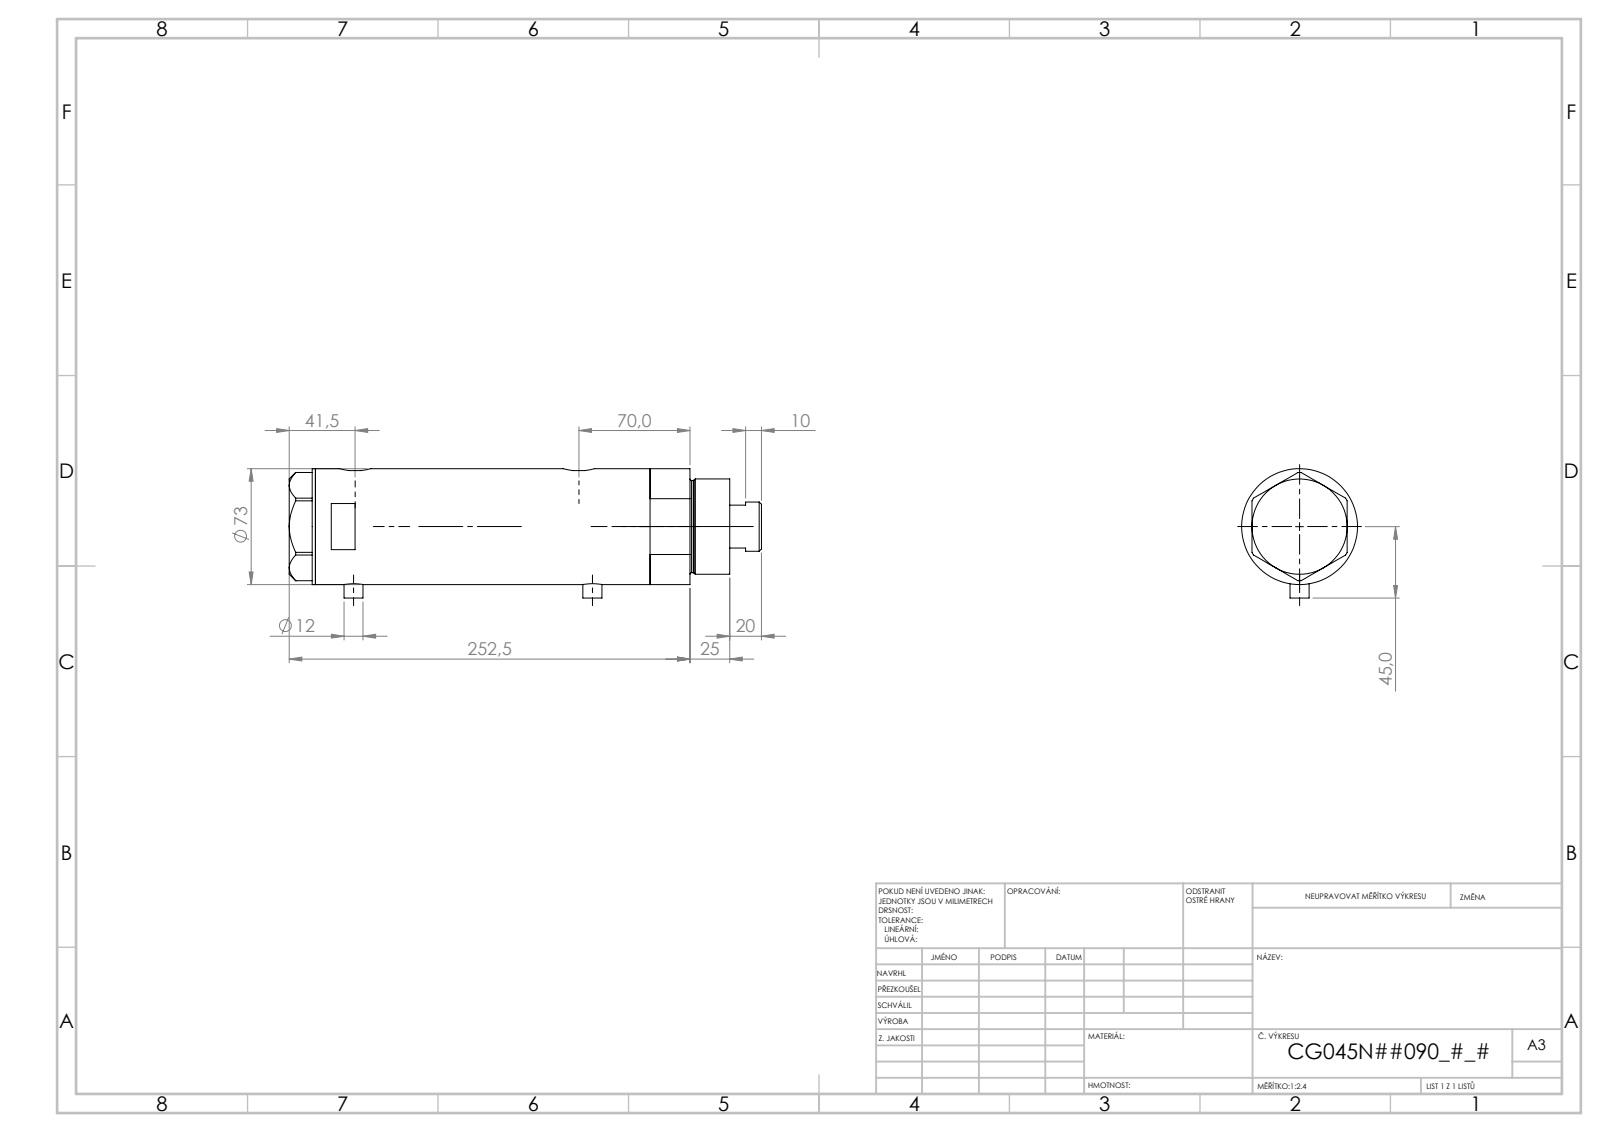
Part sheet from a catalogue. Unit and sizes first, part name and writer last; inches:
Units: inches
Overall size (bounding box): 11.083 × 2.917 × 2.874
Round holes (diameter × count): ⌀0.197 ×2, ⌀0.492 ×2, ⌀0.518 ×2, ⌀0.413 ×1, ⌀1.26 ×1, ⌀1.319 ×1, ⌀1.772 ×1, ⌀1.89 ×1, ⌀2.52 ×1
Round bosses / shafts (diameter × count): ⌀0.472 ×2, ⌀2.874 ×1, ⌀2.362 ×1, ⌀2.283 ×1, ⌀1.22 ×1
Partial cylindrical surfaces — rounded edges, fillets, slot ends (radius × count): R0.394 ×2
Main face-to-face distances: 6.187, 1.024, 5.163, 0.65, 1.673, 6.836, 9.646, 10.296, 8.622, 3.459
Hole centre spacings: 5.577, 0.039, 0.039, 0.335, 0.335, 5.203, 5.242, 5.242
Volume: 59.36 in³ · Surface area: 251.6 in²
Bodies: 4 solids, 125 faces (50 planar, 55 cylindrical, 20 other)
Part name (STEP PRODUCT): V270CG_FRONT; V270CG_BACK; V270CG_VC; V270CG_MIDDLE
STEP written by: SolidWorks 2019 (CONFIG_CONTROL_DESIGN)
